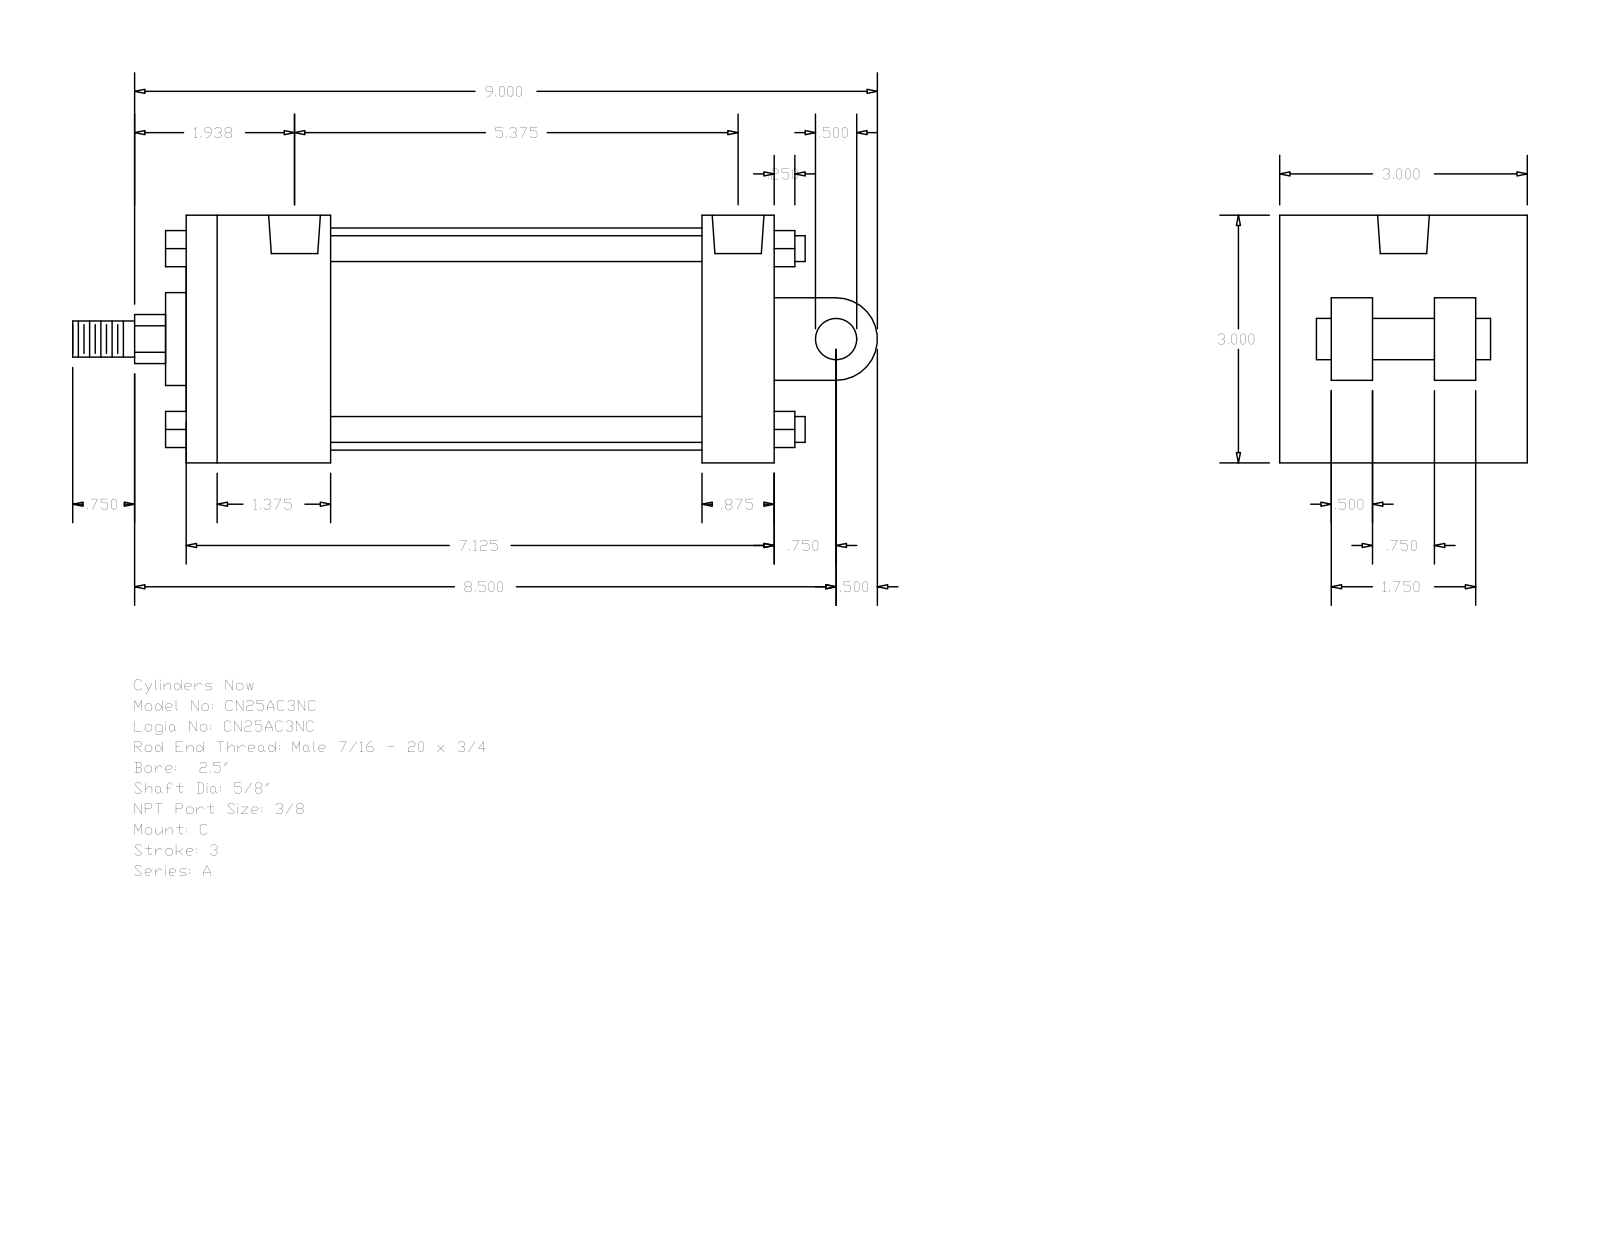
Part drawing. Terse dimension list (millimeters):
name: A_C__0250_0.625
written by: GSSL Pune (CONFIG_CONTROL_DESIGN)
unit: mm
bodies: 0 solids, 135 faces (102 planar, 33 cylindrical, 0 other)
size: 247.65 × 76.2 × 76.2
holes: 4× ⌀5.56, 2× ⌀15.93
bosses: 4× ⌀7.94, 1× ⌀68.33, 1× ⌀28.57, 1× ⌀15.88, 1× ⌀12.7, 1× ⌀11.11
rounds: 1× R7.54, 1× R12.7
face distances: 76.2, 180.97, 44.45, 158.74, 114.29, 136.52, 22.23, 50.8, 12.7, 25.4
hole spacings: 2.38, 138.91, 141.29, 136.53
